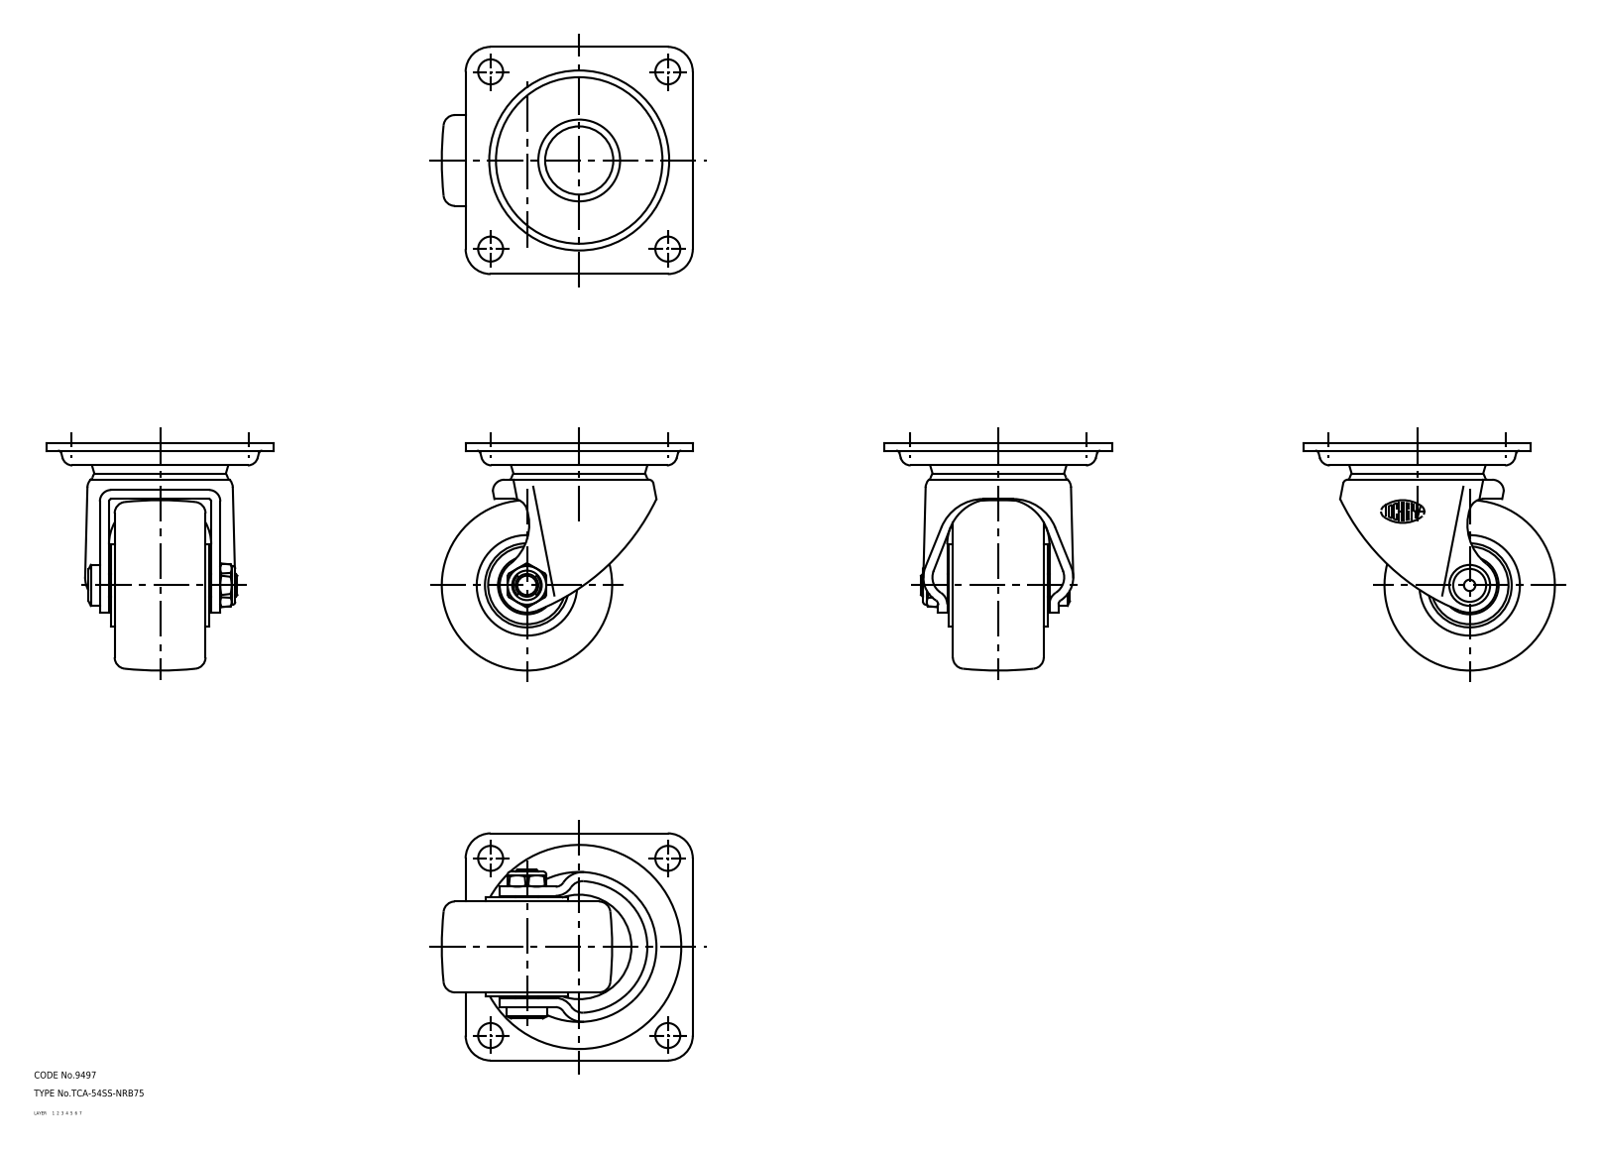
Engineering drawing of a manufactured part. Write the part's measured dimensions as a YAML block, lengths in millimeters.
part_name: "seal; nut; main shaft; wheel (+3 more)"
step_written_by: "CADfix (AUTOMOTIVE_DESIGN)"
units: millimeters
bodies: {solids: 7, faces: 227, planar: 0, cylindrical: 0, other: 227}
overall_size: [110.5, 100, 100]
volume: 288035
surface_area: 74449
